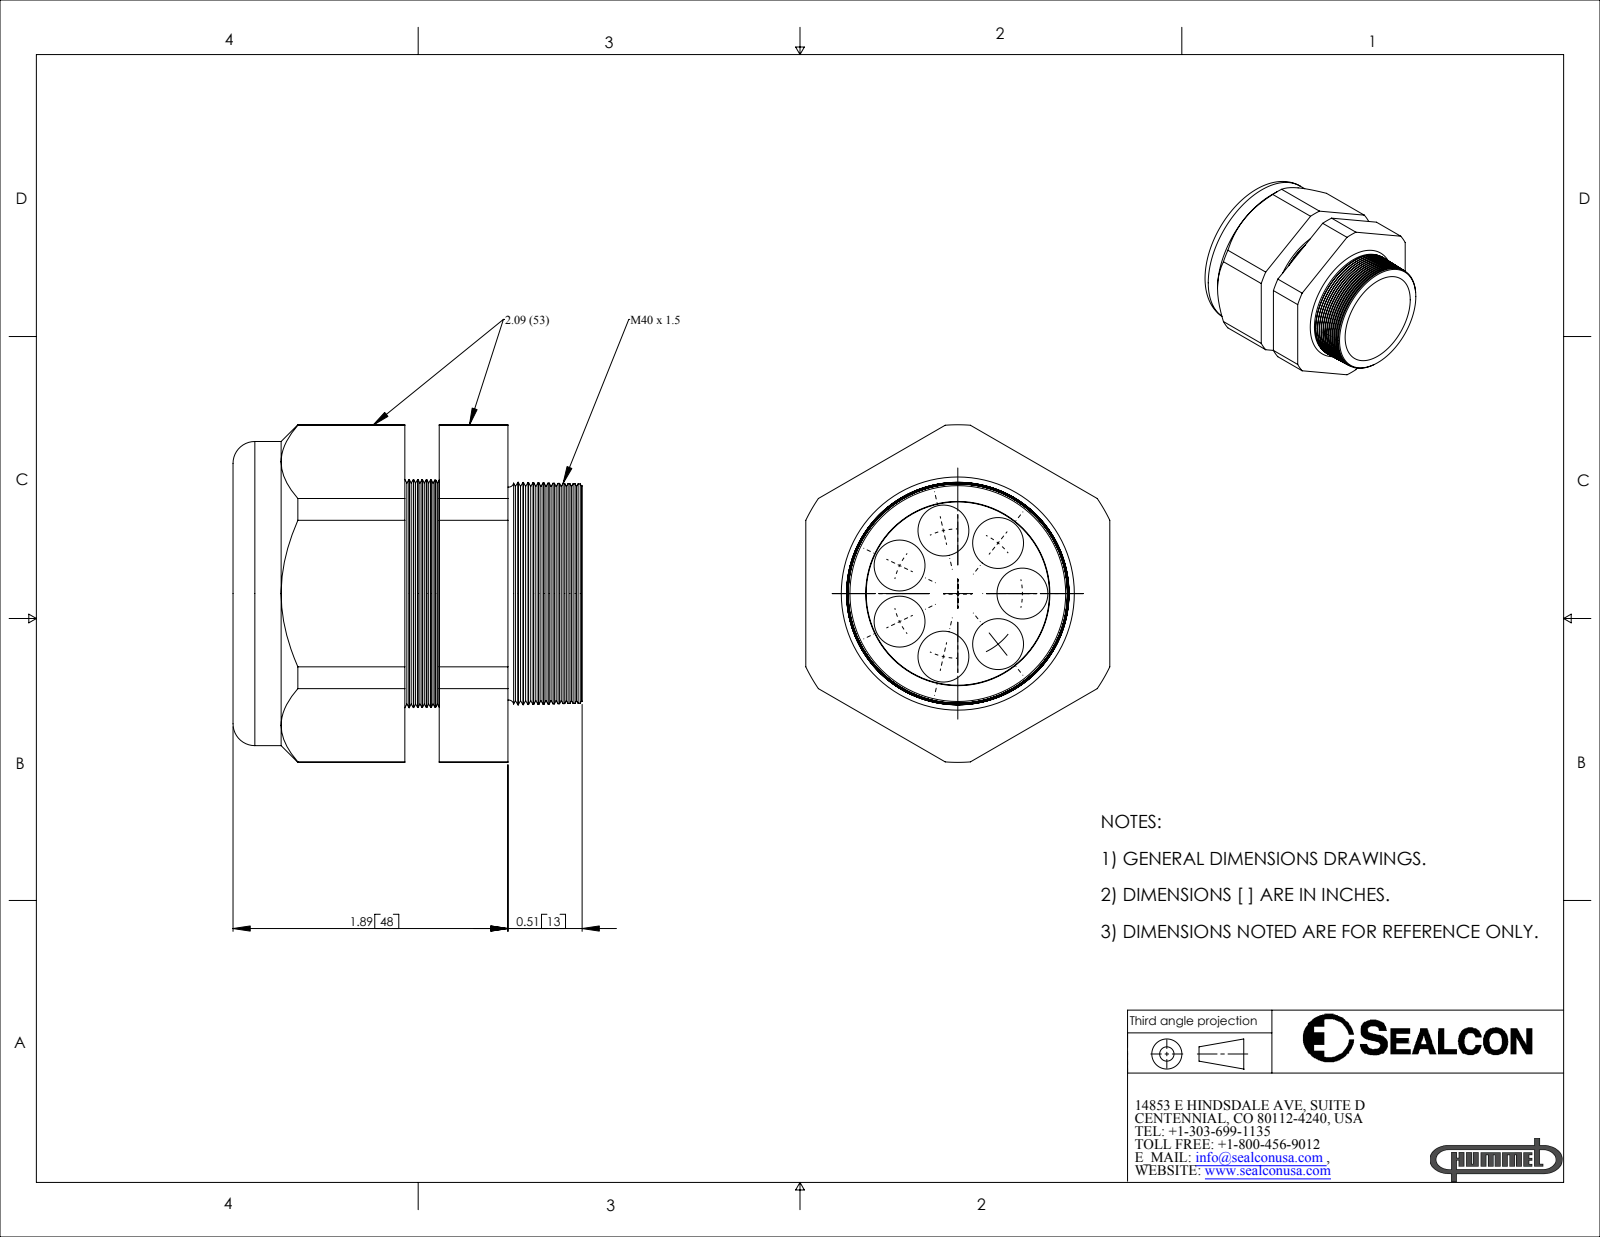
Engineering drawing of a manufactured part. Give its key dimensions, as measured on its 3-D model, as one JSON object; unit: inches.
{"part_name": "CD40M2-BK", "step_written_by": "SolidWorks 2007 (CONFIG_CONTROL_DESIGN)", "units": "inches", "bodies": {"solids": 2, "faces": 203, "planar": 21, "cylindrical": 34, "other": 148}, "overall_size": [2.4, 2.32, 2.09], "volume_in3": 4.673, "surface_area_in2": 42.51, "round_holes": [[0.35, 7], [1.24, 1], [1.26, 1]], "round_bosses_or_shafts": [[2.09, 1]], "partial_cylinders_radius": [[1.16, 1]], "face_to_face_distances": [2.09, 0.237, 0.709, 0.472, 1.181, 1.418, 1.89, 0.5, 0.681, 0.918], "hole_center_spacings": [0.695, 0.444, 0.385, 0.867, 0.386, 0.866, 0.444, 0.694]}
